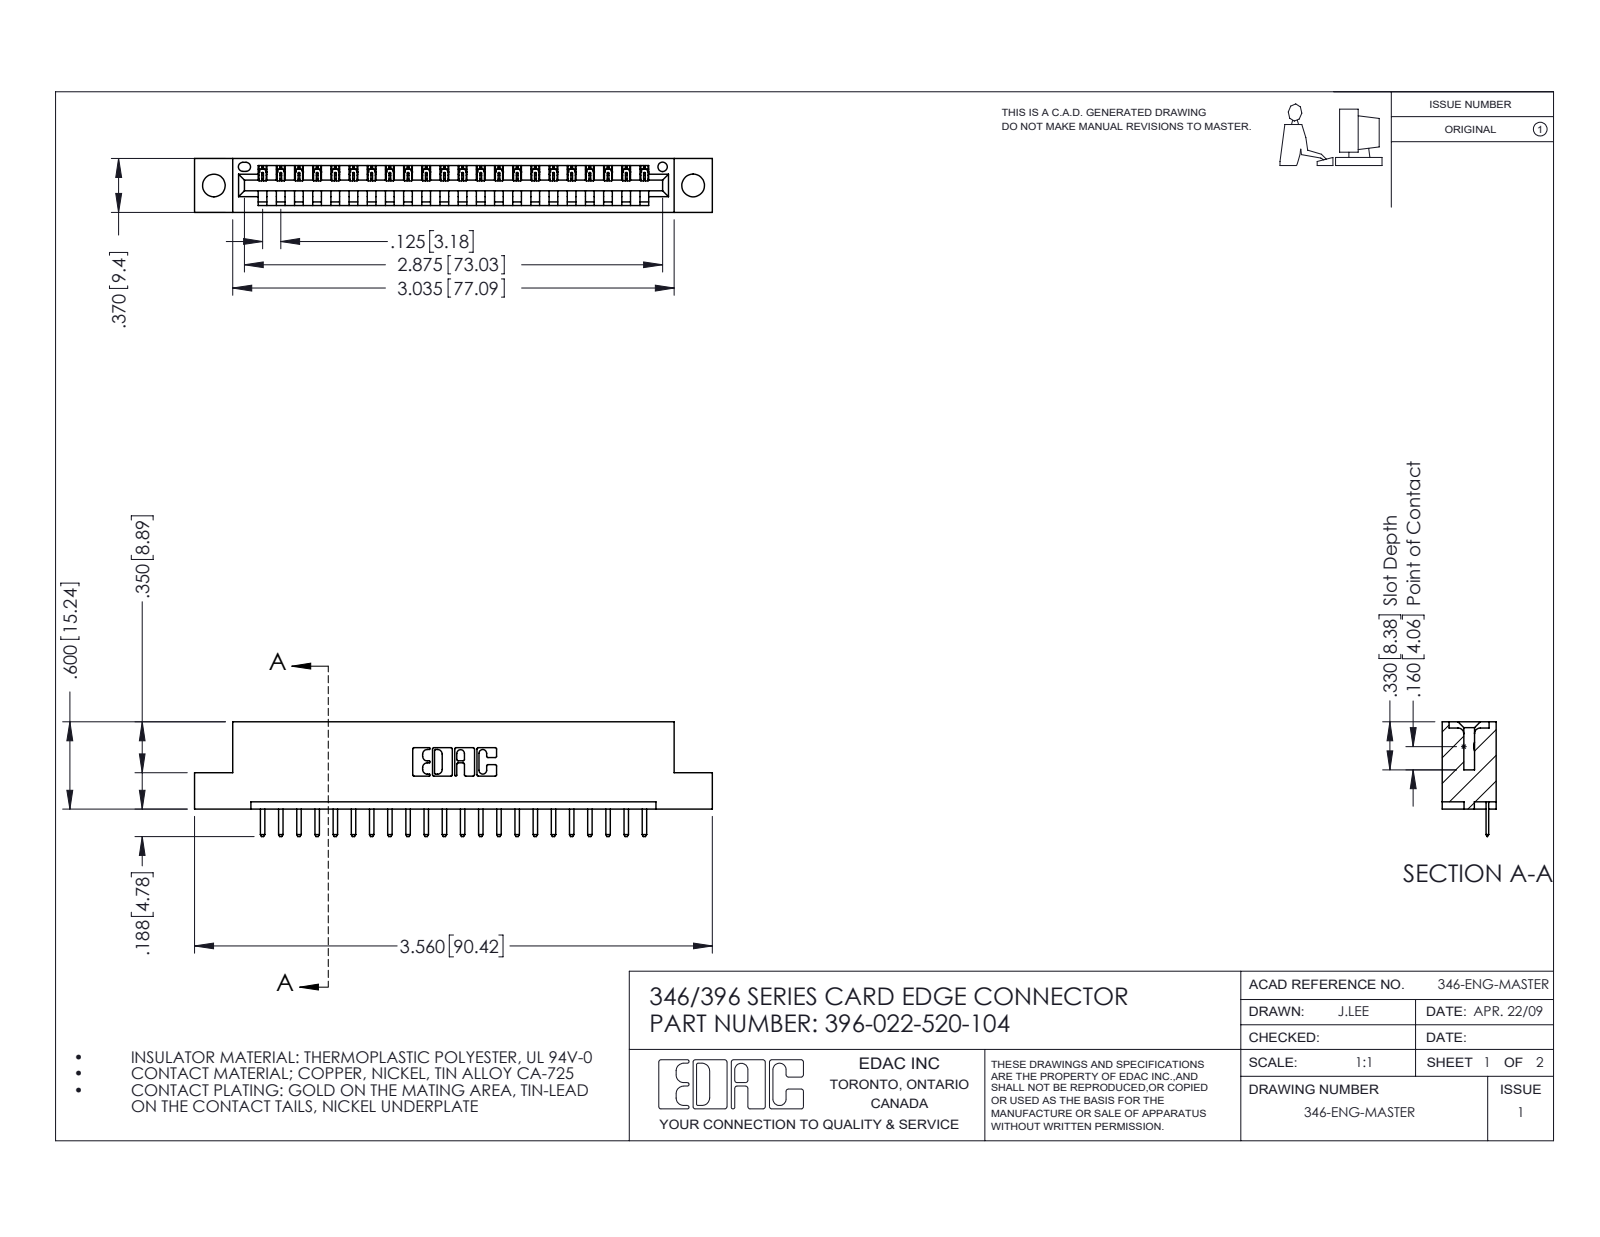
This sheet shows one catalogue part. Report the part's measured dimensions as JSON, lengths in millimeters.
{"part_name": "345-292-001_345-293-120; 396-022-520-104; 346 Part_Flush Mounting Lugs - 0.156 Dia-TH", "step_written_by": "SolidWorks 2016 (CONFIG_CONTROL_DESIGN)", "units": "millimeters", "bodies": {"solids": 23, "faces": 1486, "planar": 1000, "cylindrical": 486, "other": 0}, "overall_size": [90.4, 20, 9.4], "volume_mm3": 8370, "surface_area_mm2": 9832, "round_holes": [[4, 2], [1.6, 1]], "partial_cylinders_radius": [[0.3, 46], [0.2, 44], [0.3, 22], [0.2, 6], [0.8, 6], [0.7, 3], [0.8, 2], [1, 2]], "face_to_face_distances": [1.2, 8.2, 9.4, 6.4, 3.8, 5.6, 2.5, 4.4, 1.8, 7.6], "hole_center_spacings": [6.2, 78.4, 83.7]}
